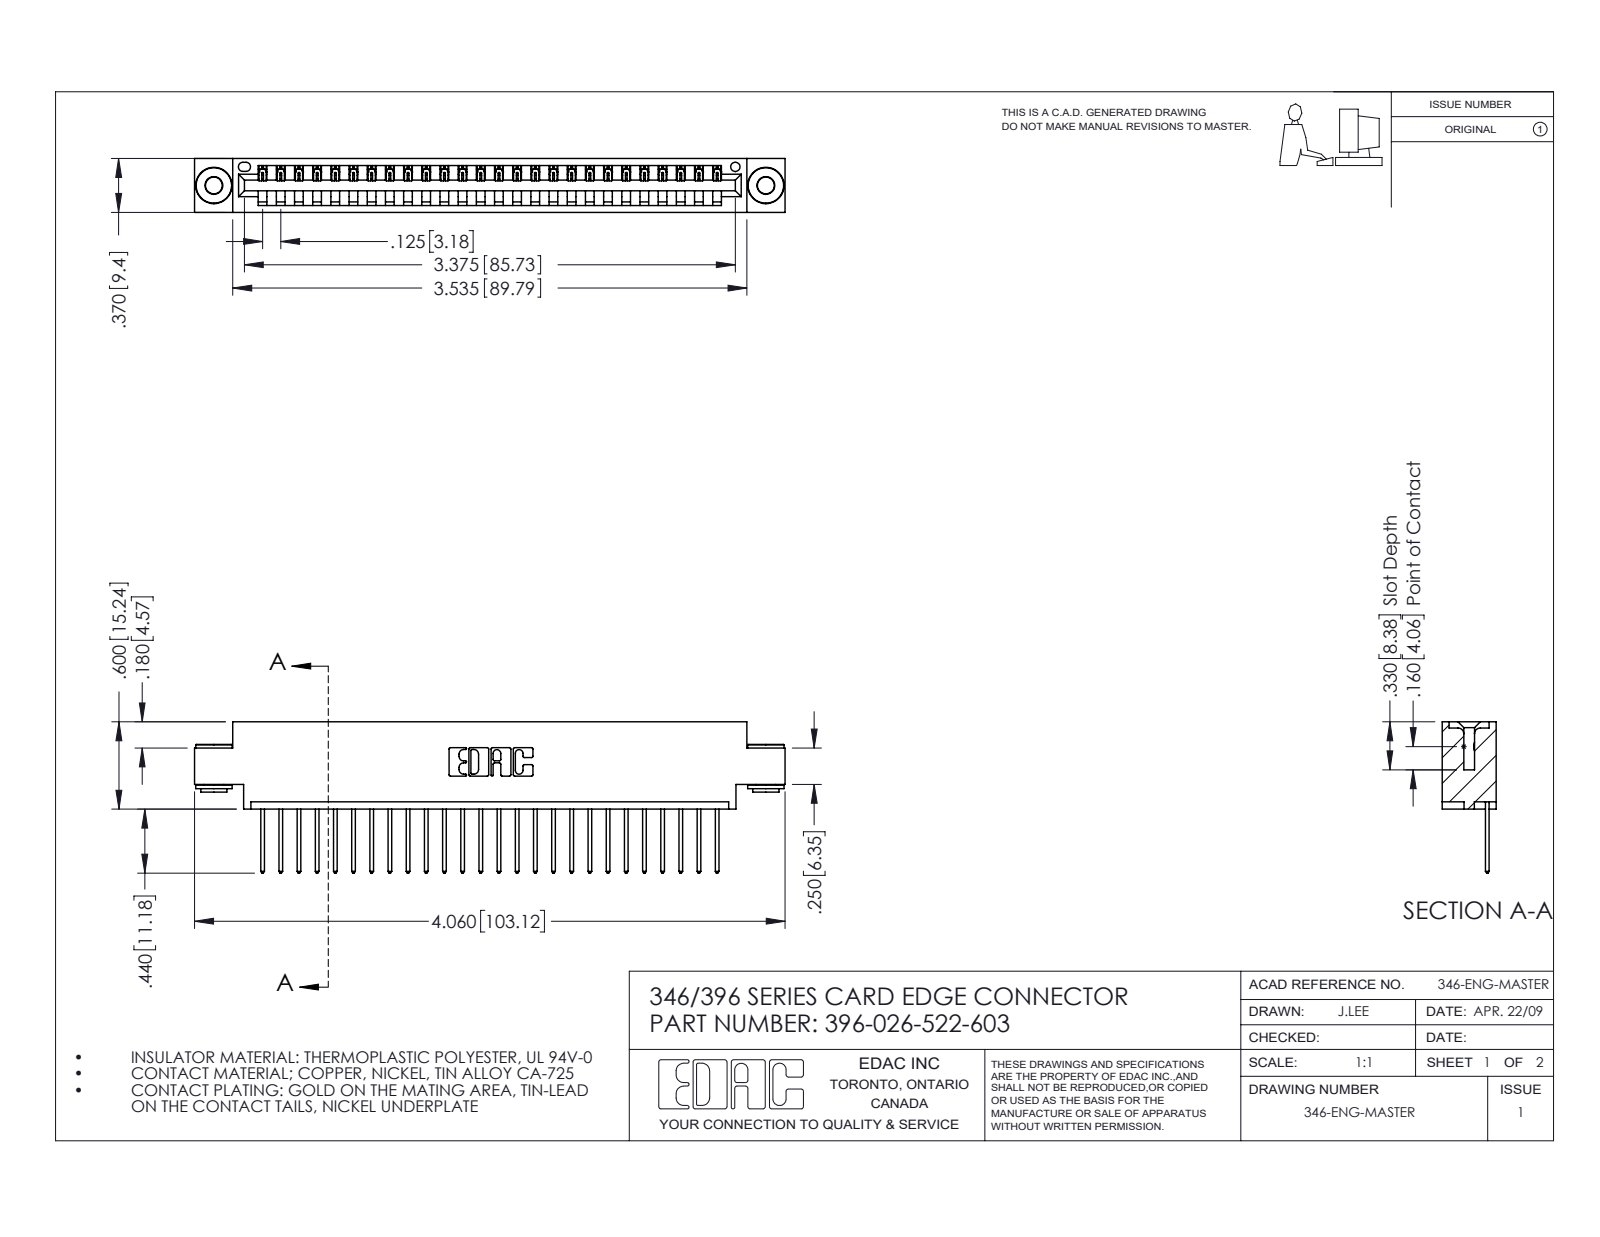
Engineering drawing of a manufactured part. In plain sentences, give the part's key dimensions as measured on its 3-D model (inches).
The part is named "345-292-001_345-293-122; 396-026-522-603; 345-250-002_345-250-002-102; 346 Part_0.170 Offset - 0.156 Dia-TH". Its 3-D file was written by "SolidWorks 2016 (CONFIG_CONTROL_DESIGN)". It is 29 solids with 1672 faces: 1130 planar, 534 cylindrical and 8 other. Overall it measures 4.06 by 1.04 by 0.37 inches. Its volume is 0.588 cubic inches and its surface area 19.12 square inches. Round holes: 2 of diameter 0.116, 2 of diameter 0.156, 1 of diameter 0.064. Round bosses or shafts: 2 of diameter 0.25, 2 of diameter 0.18, 2 of diameter 0.136. Partial cylindrical surfaces (rounded edges, fillets, slot ends): 52 of radius 0.006, 52 of radius 0.01, 22 of radius 0.01, 6 of radius 0.007, 6 of radius 0.031, 3 of radius 0.026, 2 of radius 0.031, 2 of radius 0.04. The main face-to-face distances are 0.048, 0.322, 0.37, 0.25, 0.025, 0.072, 0.298, 0.148, 0.222, 0.1. The hole center spacings are 0.246, 3.587, 3.795.
